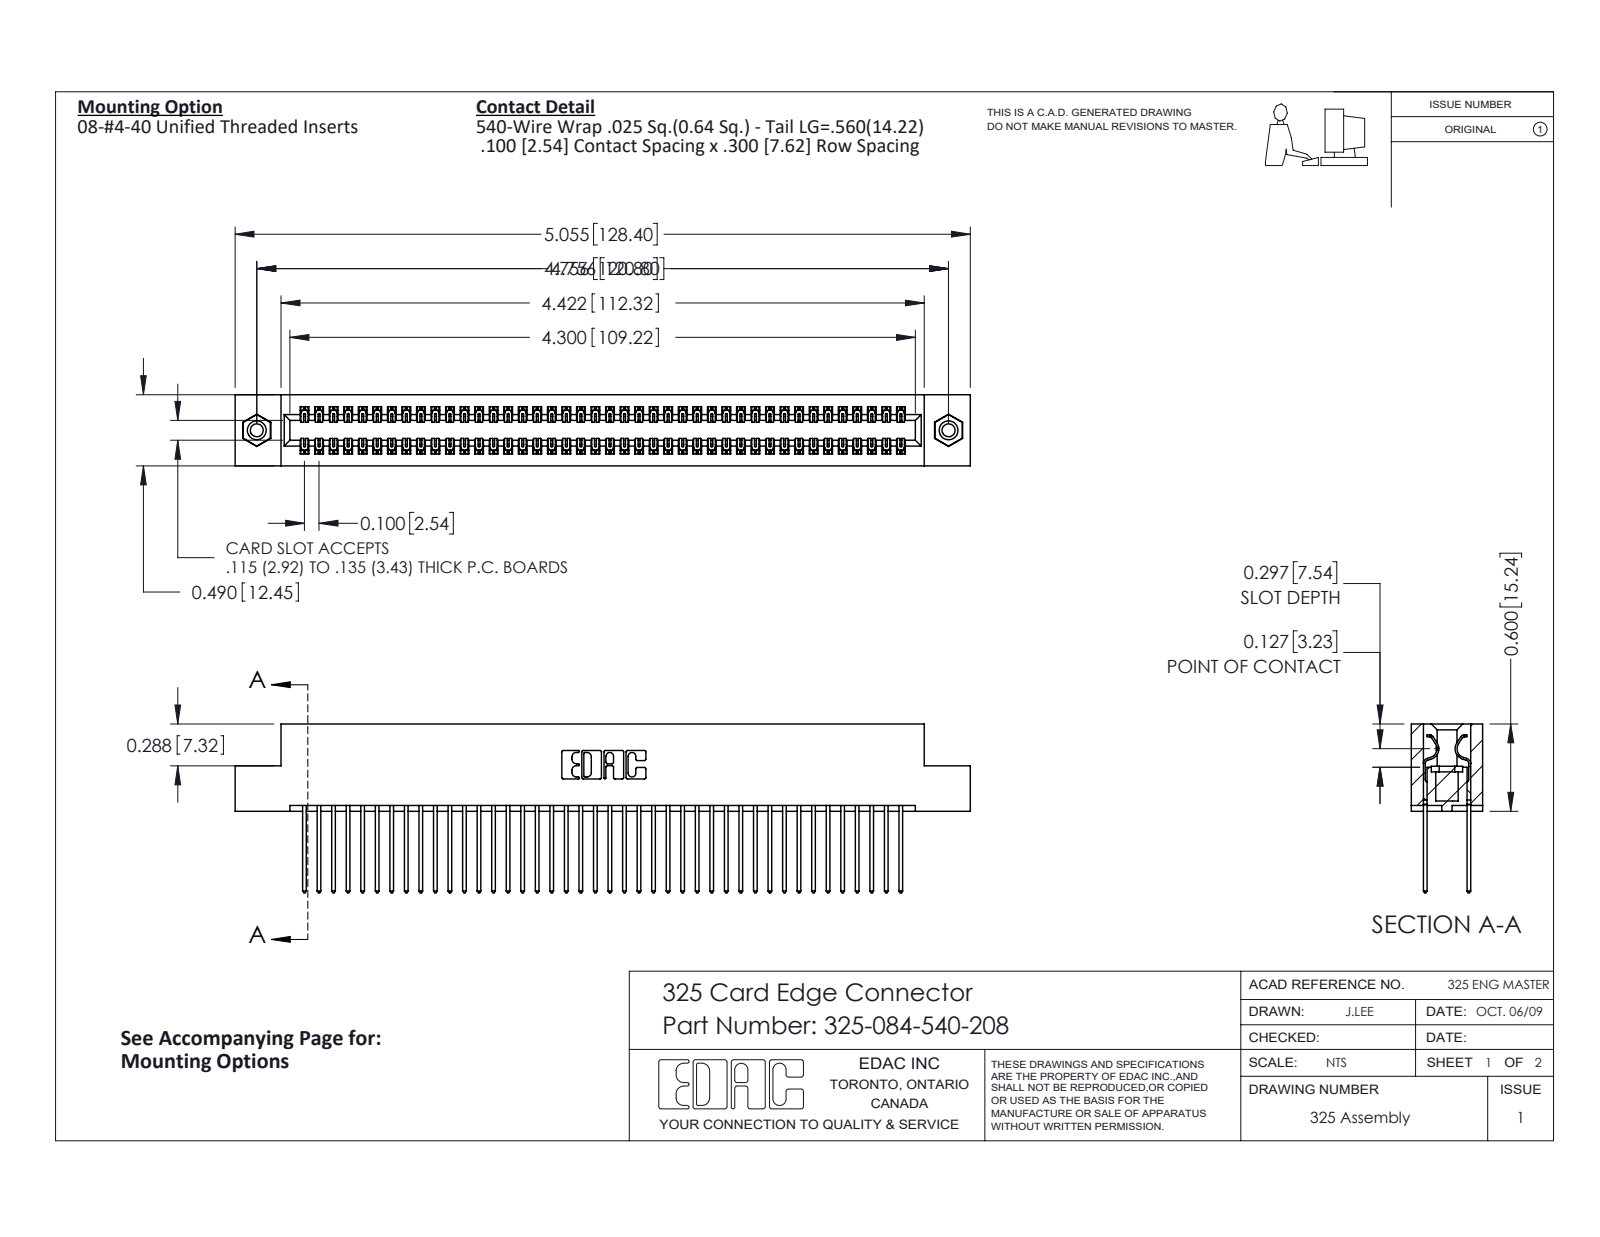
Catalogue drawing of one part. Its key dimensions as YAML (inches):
part_name: "325-084-540-208; 325-292-001_325-293-140; 345-250-001_345-250-003-102; 325 Part_TI"
step_written_by: "SolidWorks 2016 (CONFIG_CONTROL_DESIGN)"
units: inches
bodies: {solids: 87, faces: 4542, planar: 3126, cylindrical: 1400, other: 16}
overall_size: [5.055, 1.16, 0.49]
volume: 1.031
surface_area: 34.05
round_holes:
  - {diameter: 0.089, count: 2}
  - {diameter: 0.125, count: 2}
  - {diameter: 0.16, count: 2}
round_bosses_or_shafts:
  - {diameter: 0.155, count: 2}
partial_cylinders:
  - {radius: 0.006, count: 126}
  - {radius: 0.01, count: 84}
  - {radius: 0.01, count: 22}
  - {radius: 0.007, count: 6}
  - {radius: 0.031, count: 6}
  - {radius: 0.026, count: 3}
  - {radius: 0.014, count: 2}
  - {radius: 0.022, count: 2}
face_to_face_distances: [0.083, 0.407, 0.3, 0.107, 0.383, 0.025, 0.49, 0.325, 0.275, 0.56]
hole_center_spacings: [4.756]
